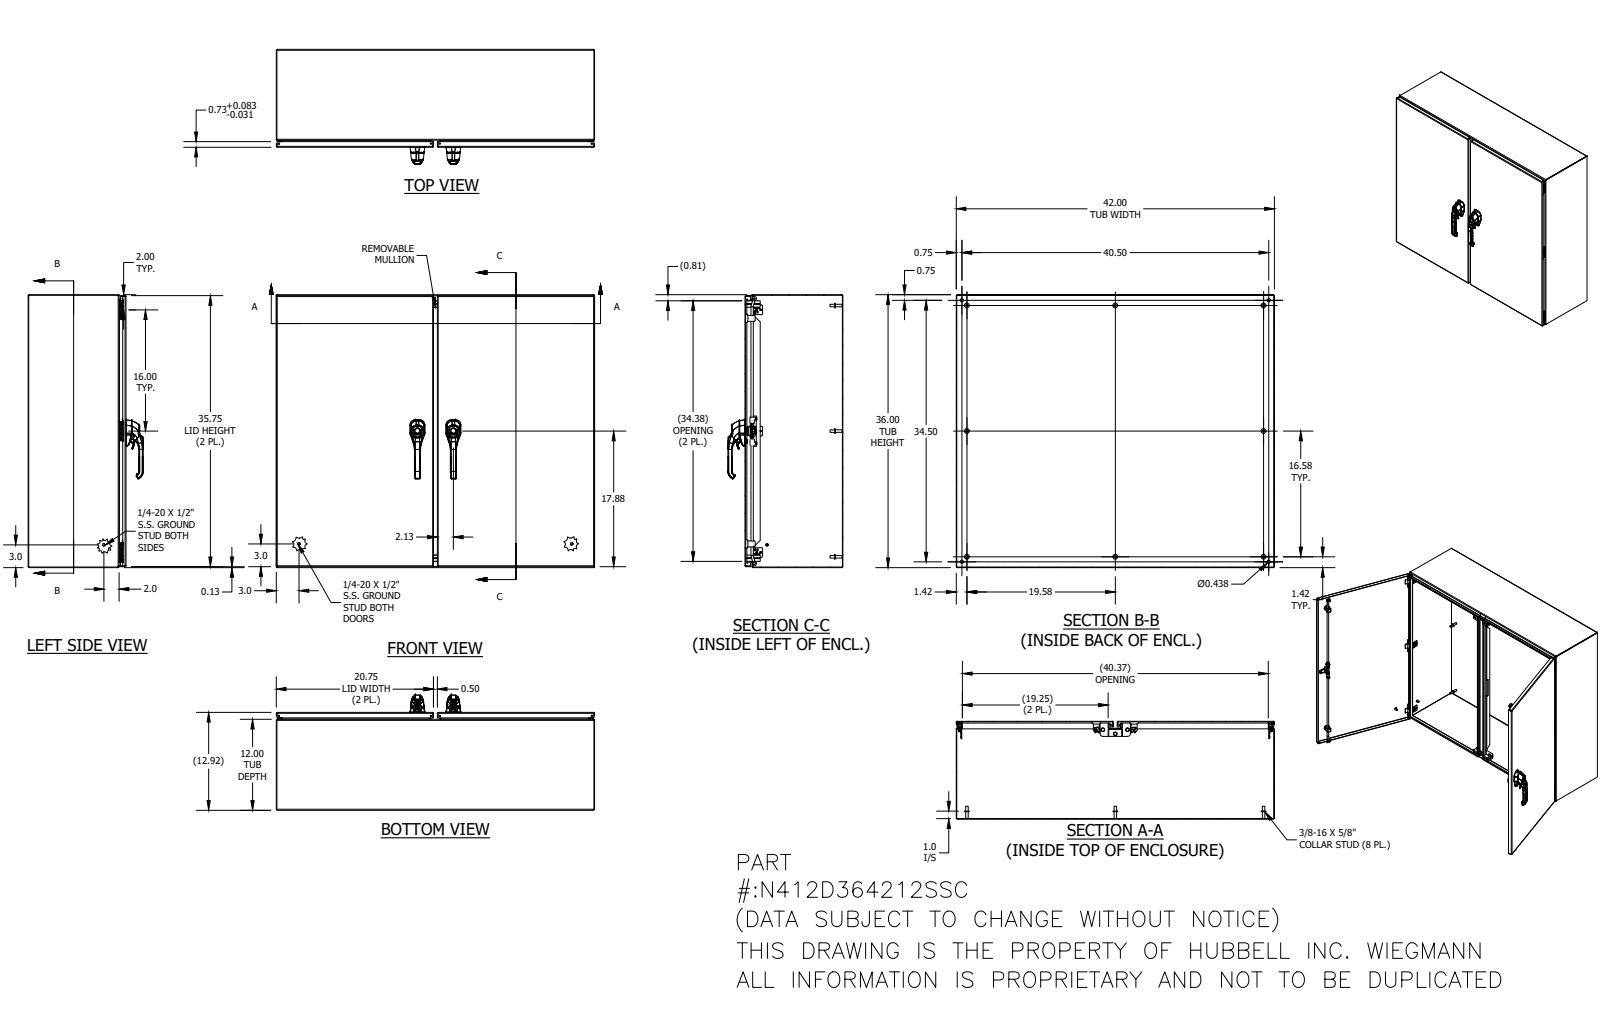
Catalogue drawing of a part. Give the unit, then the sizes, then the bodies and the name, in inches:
Units: inches
Overall size (bounding box): 42 × 36 × 15.166
Round holes (diameter × count): ⌀0.16 ×14, ⌀0.093 ×12, ⌀0.136 ×12, ⌀0.167 ×12, ⌀0.188 ×12, ⌀0.197 ×8, ⌀0.156 ×6, ⌀0.159 ×6, ⌀0.165 ×6, ⌀0.186 ×6, ⌀0.213 ×6, ⌀0.28 ×6
Round bosses / shafts (diameter × count): ⌀0.25 ×24, ⌀0.36 ×12, ⌀0.32 ×12, ⌀0.256 ×12, ⌀0.236 ×12, ⌀0.164 ×12, ⌀0.131 ×12, ⌀0.625 ×8
Partial cylindrical surfaces — rounded edges, fillets, slot ends (radius × count): R0.02 ×266, R0.012 ×173, R0.05 ×64, R0.031 ×44, R0.125 ×36, R0.118 ×33, R0.016 ×26, R0.079 ×25
Main face-to-face distances: 0.074, 12.843, 12.769, 12.917, 35.926, 41.926, 35.852, 36, 41.852, 42
Hole centre spacings: 16, 44.198, 4.748, 0.66, 2.327, 4.83, 16.004, 18.267
Volume: 439.8 in³ · Surface area: 11 444 in²
Bodies: 161 solids, 7486 faces (2508 planar, 2682 cylindrical, 2296 other)
Part name (STEP PRODUCT): N412D364212SSC; N412D364212SSCBTB; N412D3612SSCLRS; N412D3642SSCLDR (+8 more)
STEP written by: Autodesk Inventor 2020 (AUTOMOTIVE_DESIGN)
